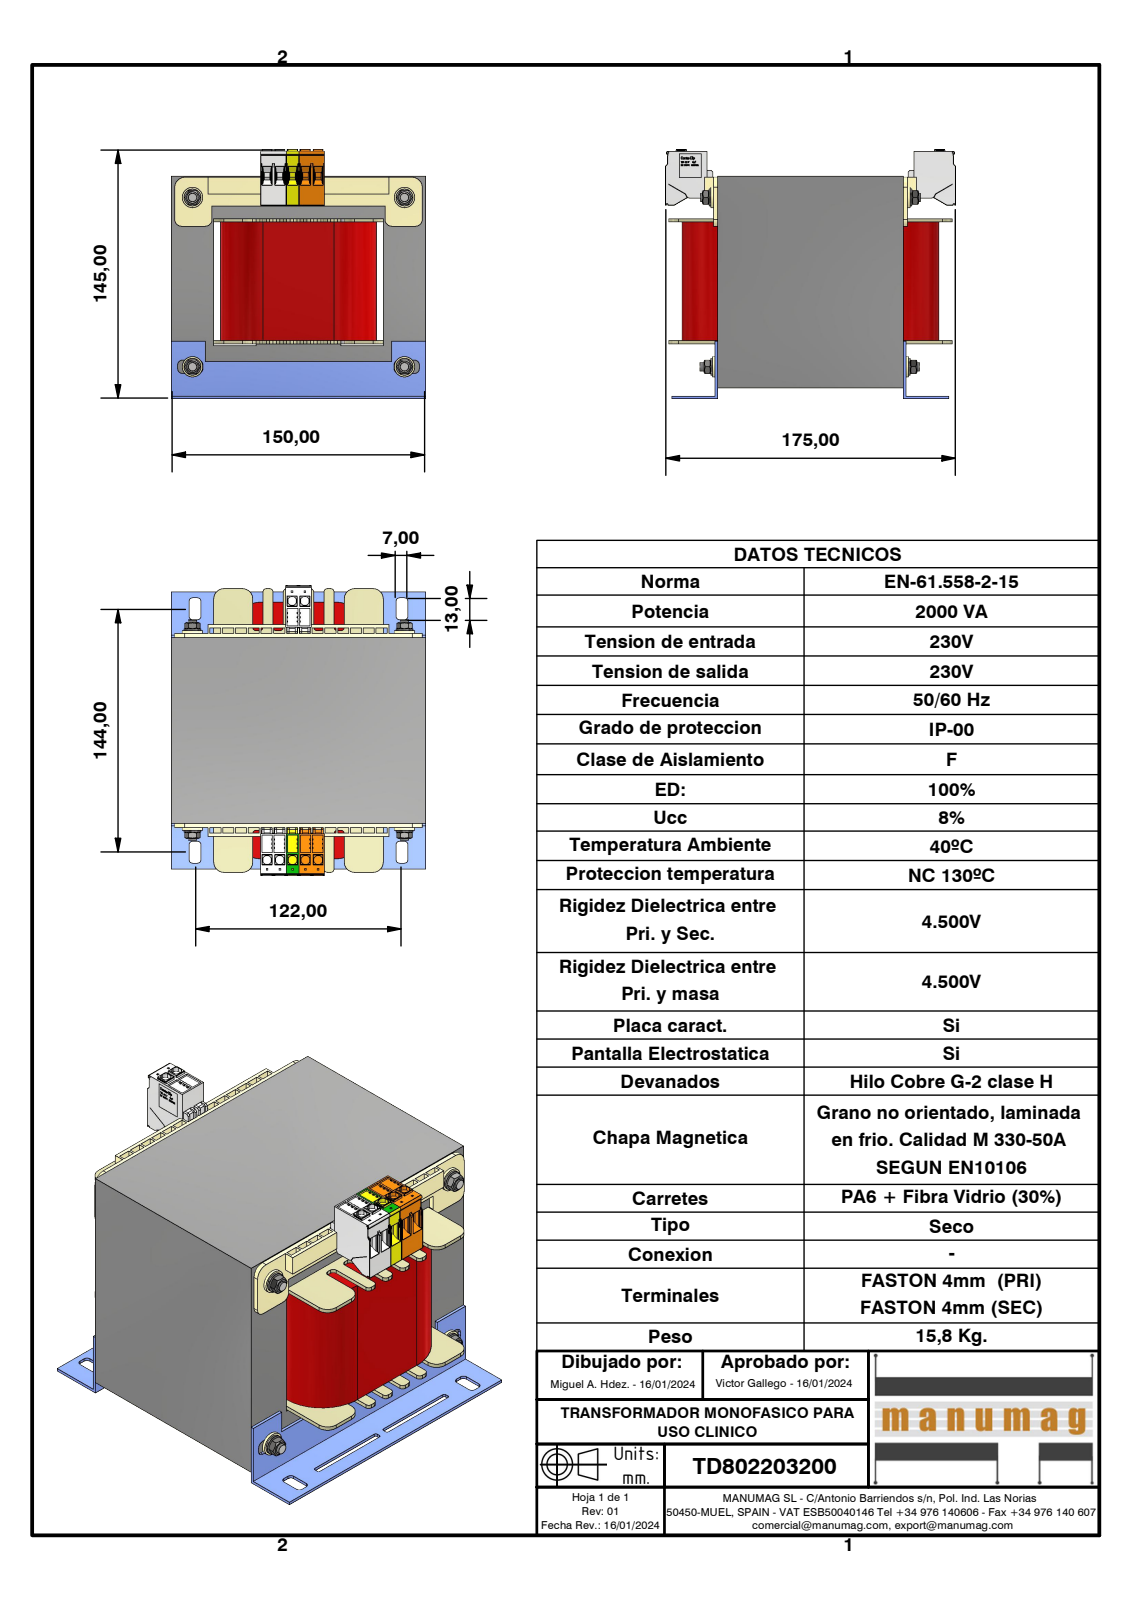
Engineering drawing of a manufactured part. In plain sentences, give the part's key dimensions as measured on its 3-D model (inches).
The part is named "TD802203200; EI150 x 125 - 110 (RC50); AF50DIN; EI150 (+8 more)". Its 3-D file was written by "Autodesk Inventor 2023 (AUTOMOTIVE_DESIGN)". It is 38 solids with 6998 faces: 5761 planar, 855 cylindrical and 382 other. Overall it measures 6.768 by 5.906 by 5.803 inches. Its volume is 140.7 cubic inches and its surface area 494 square inches. Round holes: 4 of diameter 0.163, 4 of diameter 0.197, 4 of diameter 0.209, 4 of diameter 0.315. Round bosses or shafts: 4 of diameter 0.472, 4 of diameter 0.394, 4 of diameter 0.232. Partial cylindrical surfaces (rounded edges, fillets, slot ends): 296 of radius 0.006, 88 of radius 0.008, 52 of radius 0.079, 24 of radius 0.039, 22 of radius 0.02, 12 of radius 0.012, 10 of radius 0.236, 8 of radius 0.118. The main face-to-face distances are 3.937, 0.984, 1.969, 4.921, 4.331, 2.953, 0.059, 5.906, 0.827, 0.039. The hole center spacings are 3.937, 4.921, 6.302.
